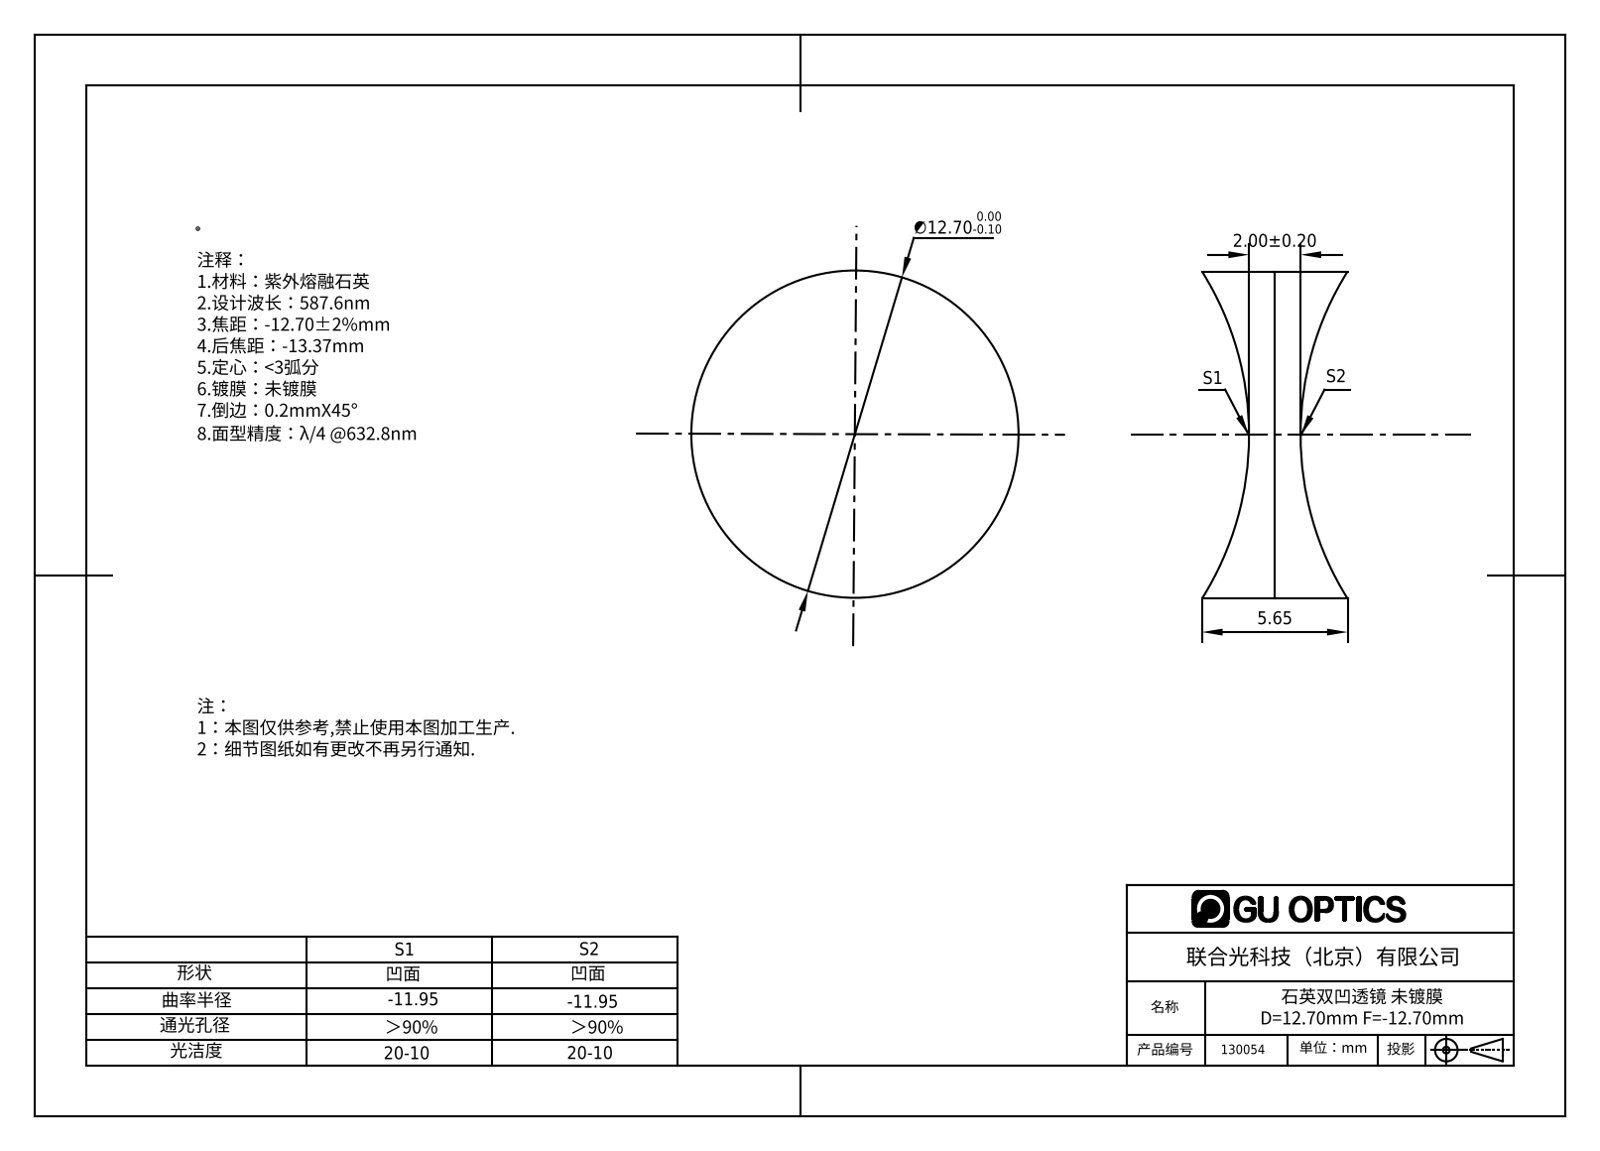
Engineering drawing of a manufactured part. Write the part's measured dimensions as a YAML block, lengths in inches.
part_name: "130054"
step_written_by: "SolidWorks 2016 (AUTOMOTIVE_DESIGN)"
units: inches
bodies: {solids: 1, faces: 6, planar: 0, cylindrical: 2, other: 4}
overall_size: [0.5, 0.5, 0.222]
volume: 0.029
surface_area: 0.775
round_bosses_or_shafts:
  - {diameter: 0.5, count: 1}
